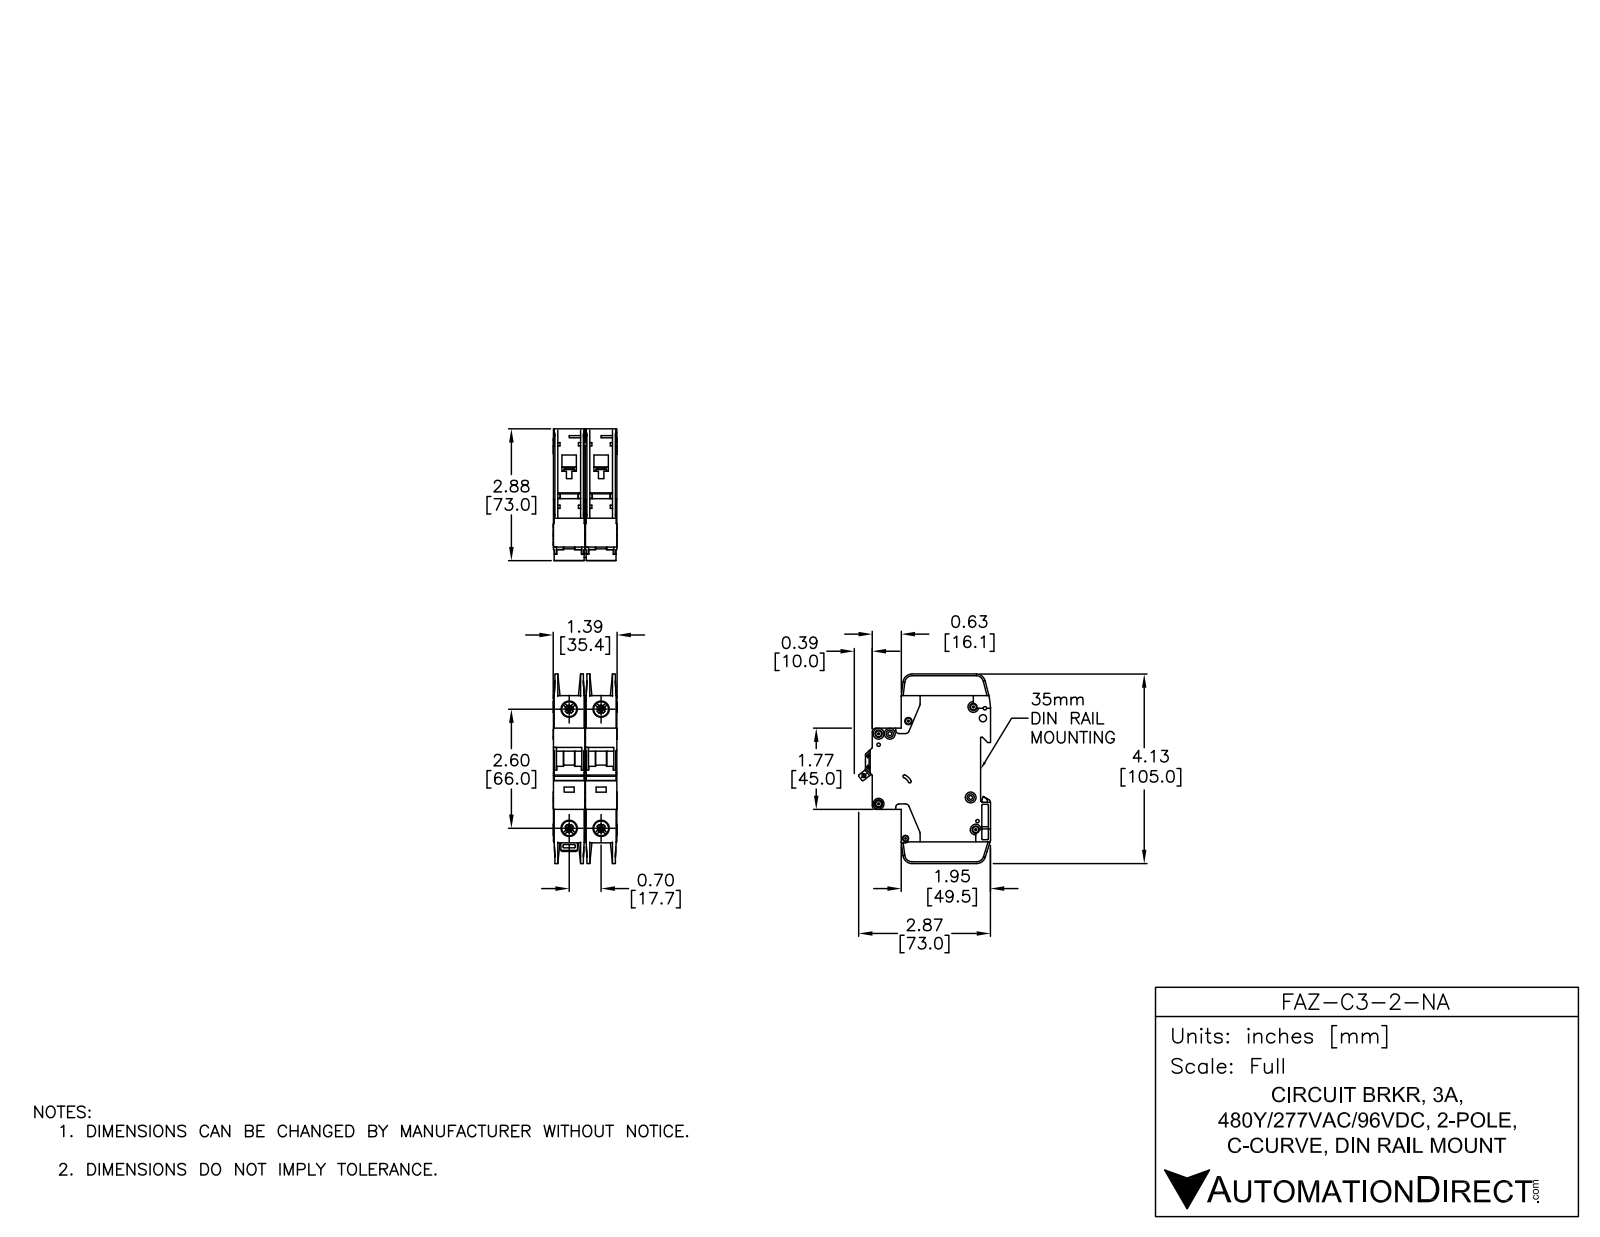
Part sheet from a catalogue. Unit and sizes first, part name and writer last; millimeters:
Units: millimetres
Overall size (bounding box): 105 × 73.04 × 35.4
Round holes (diameter × count): ⌀3.6 ×7, ⌀7.15 ×4, ⌀8.2 ×4, ⌀1.09 ×2, ⌀1.5 ×2, ⌀4 ×2, ⌀1.9 ×1, ⌀2.15 ×1, ⌀2.2 ×1, ⌀2.55 ×1, ⌀3.3 ×1, ⌀3.4 ×1
Round bosses / shafts (diameter × count): ⌀6 ×7, ⌀2.5 ×2
Partial cylindrical surfaces — rounded edges, fillets, slot ends (radius × count): R0.25 ×47, R0.5 ×24, R1 ×18, R2 ×12, R5 ×5, R1.8 ×4, R4 ×4, R0.2 ×2
Main face-to-face distances: 17.7, 17.5, 0.7, 15.05, 2.45, 1.75, 15.75, 13.3, 35.2, 17
Hole centre spacings: 6.2, 17.7, 66, 68.33, 5.19, 6.1, 8.19, 8.56
Volume: 155 390 mm³ · Surface area: 49 479 mm²
Bodies: 6 solids, 1568 faces (818 planar, 526 cylindrical, 224 other)
Part name (STEP PRODUCT): FAZ-C3-2-NA
STEP written by: SolidWorks 2014 (AUTOMOTIVE_DESIGN)
